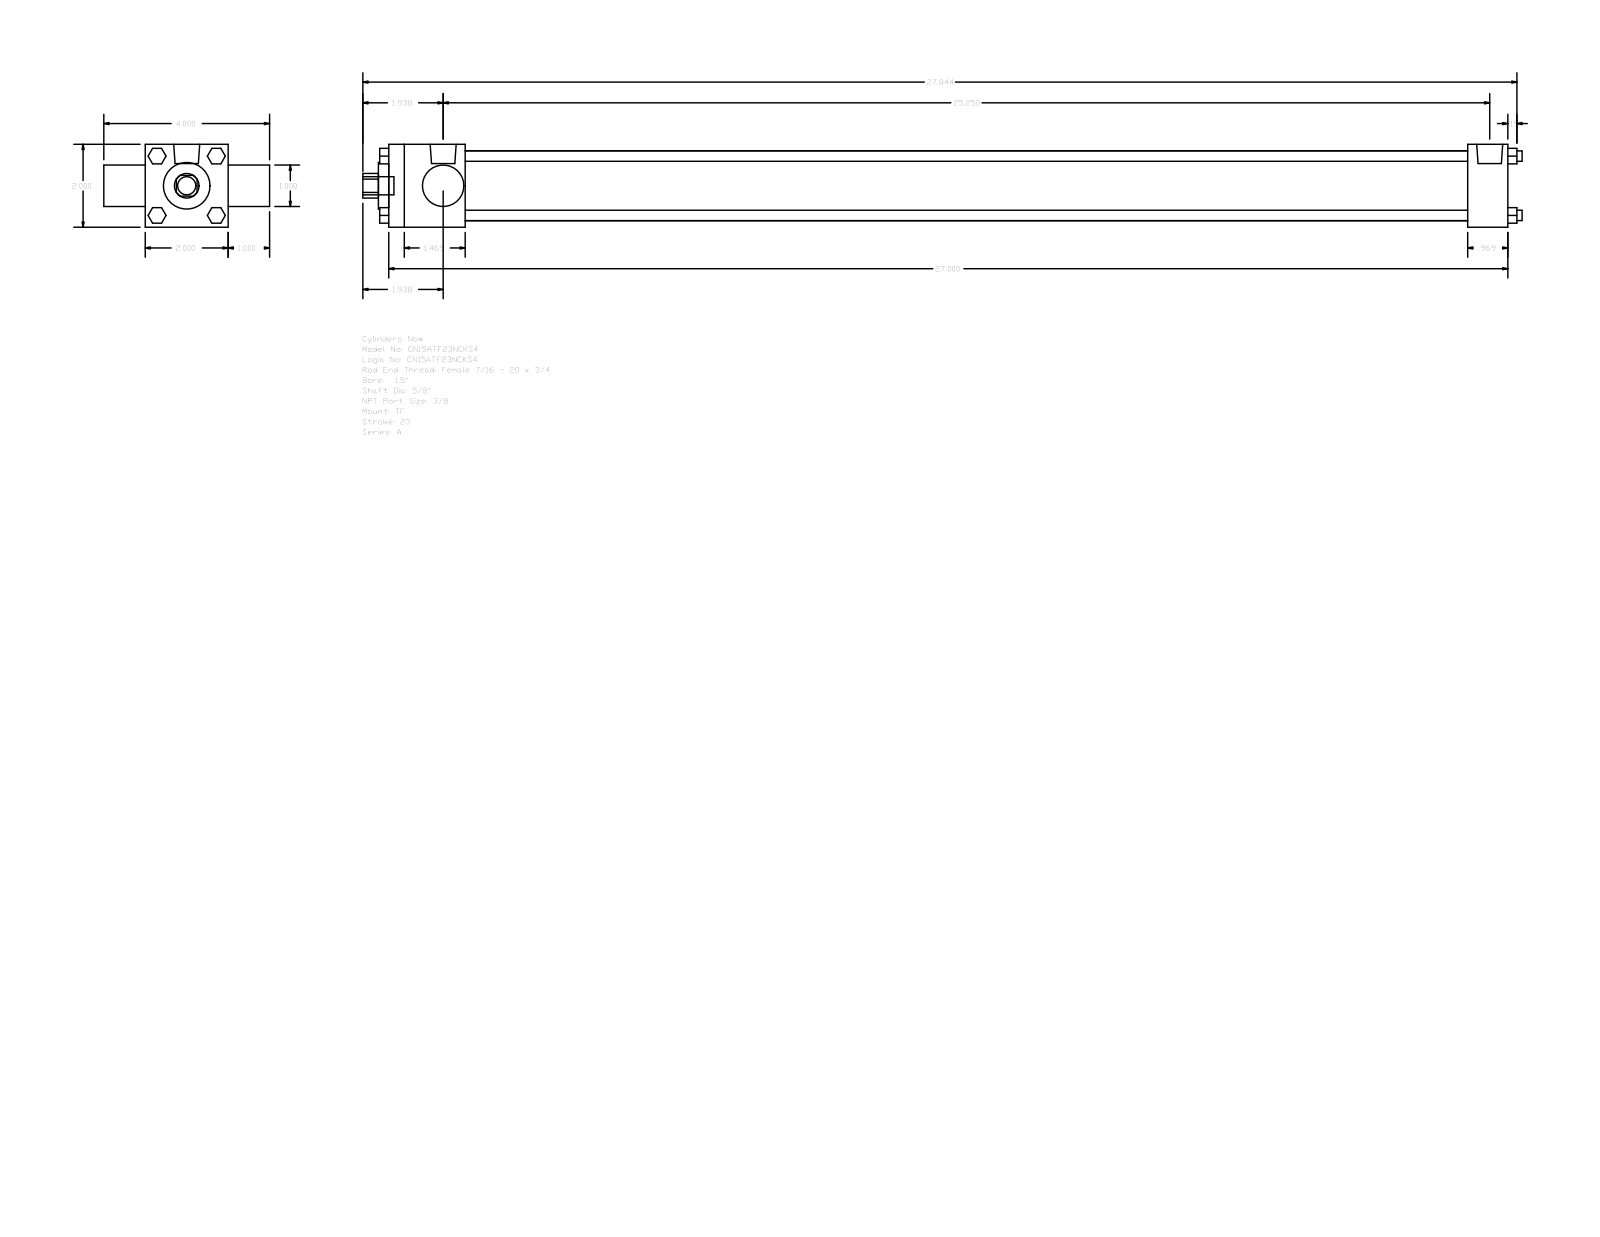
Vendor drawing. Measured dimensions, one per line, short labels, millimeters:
name: A_TF__0150_0.625
written by: GSSL Pune (CONFIG_CONTROL_DESIGN)
unit: mm
bodies: 0 solids, 120 faces (92 planar, 28 cylindrical, 0 other)
size: 710.41 × 101.6 × 50.8
holes: 1× ⌀15.88, 1× ⌀25.4, 1× ⌀28.57, 1× ⌀42.93
bosses: 4× ⌀6.35, 3× ⌀5.56, 2× ⌀15.93, 1× ⌀11.11
rounds: 1× R7.54
face distances: 50.8, 685.79, 25.4, 76.2, 46.83, 661.19, 614.36, 638.96, 24.6, 9.52
